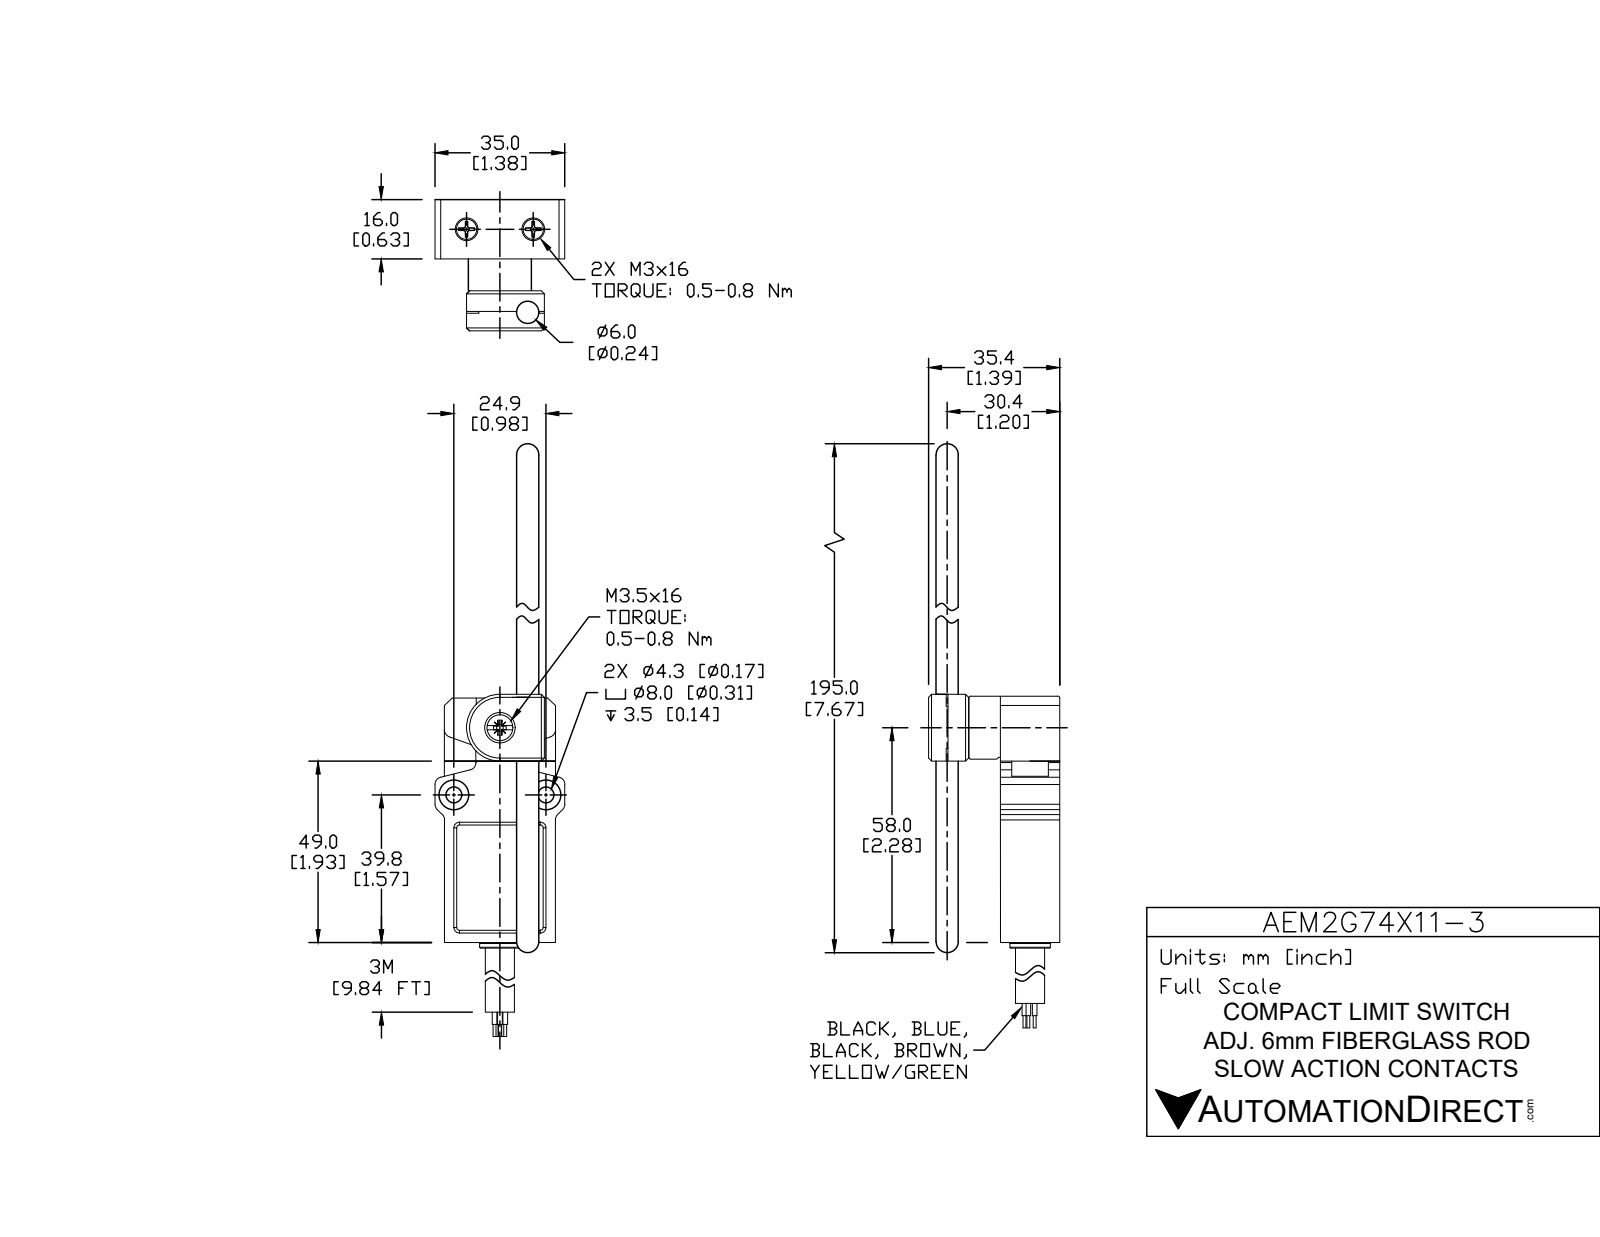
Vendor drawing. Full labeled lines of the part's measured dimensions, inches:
Part name (STEP PRODUCT): AEM2G74X11-3_Default
STEP written by: SolidWorks 2021 (CONFIG_CONTROL_DESIGN)
Units: inches
Bodies: 1 solid, 260 faces (146 planar, 81 cylindrical, 33 other)
Overall size (bounding box): 5.75 × 1.38 × 1.35
Volume: 2.191 in³ · Surface area: 18.57 in²
Round holes (diameter × count): ⌀0.177 ×2, ⌀0.24 ×2, ⌀0.344 ×2, ⌀0.32 ×1
Round bosses / shafts (diameter × count): ⌀0.05 ×5, ⌀0.031 ×5, ⌀0.67 ×1, ⌀0.43 ×1, ⌀0.31 ×1, ⌀0.289 ×1
Partial cylindrical surfaces — rounded edges, fillets, slot ends (radius × count): R0.015 ×20, R0.08 ×12, R0.03 ×8, R0.355 ×1
Main face-to-face distances: 0.03, 0.6, 0.12, 0.63, 1.18, 0.57, 1.085, 0.75, 0.575, 0.51
Hole centre spacings: 0.863, 0.71, 0.98
